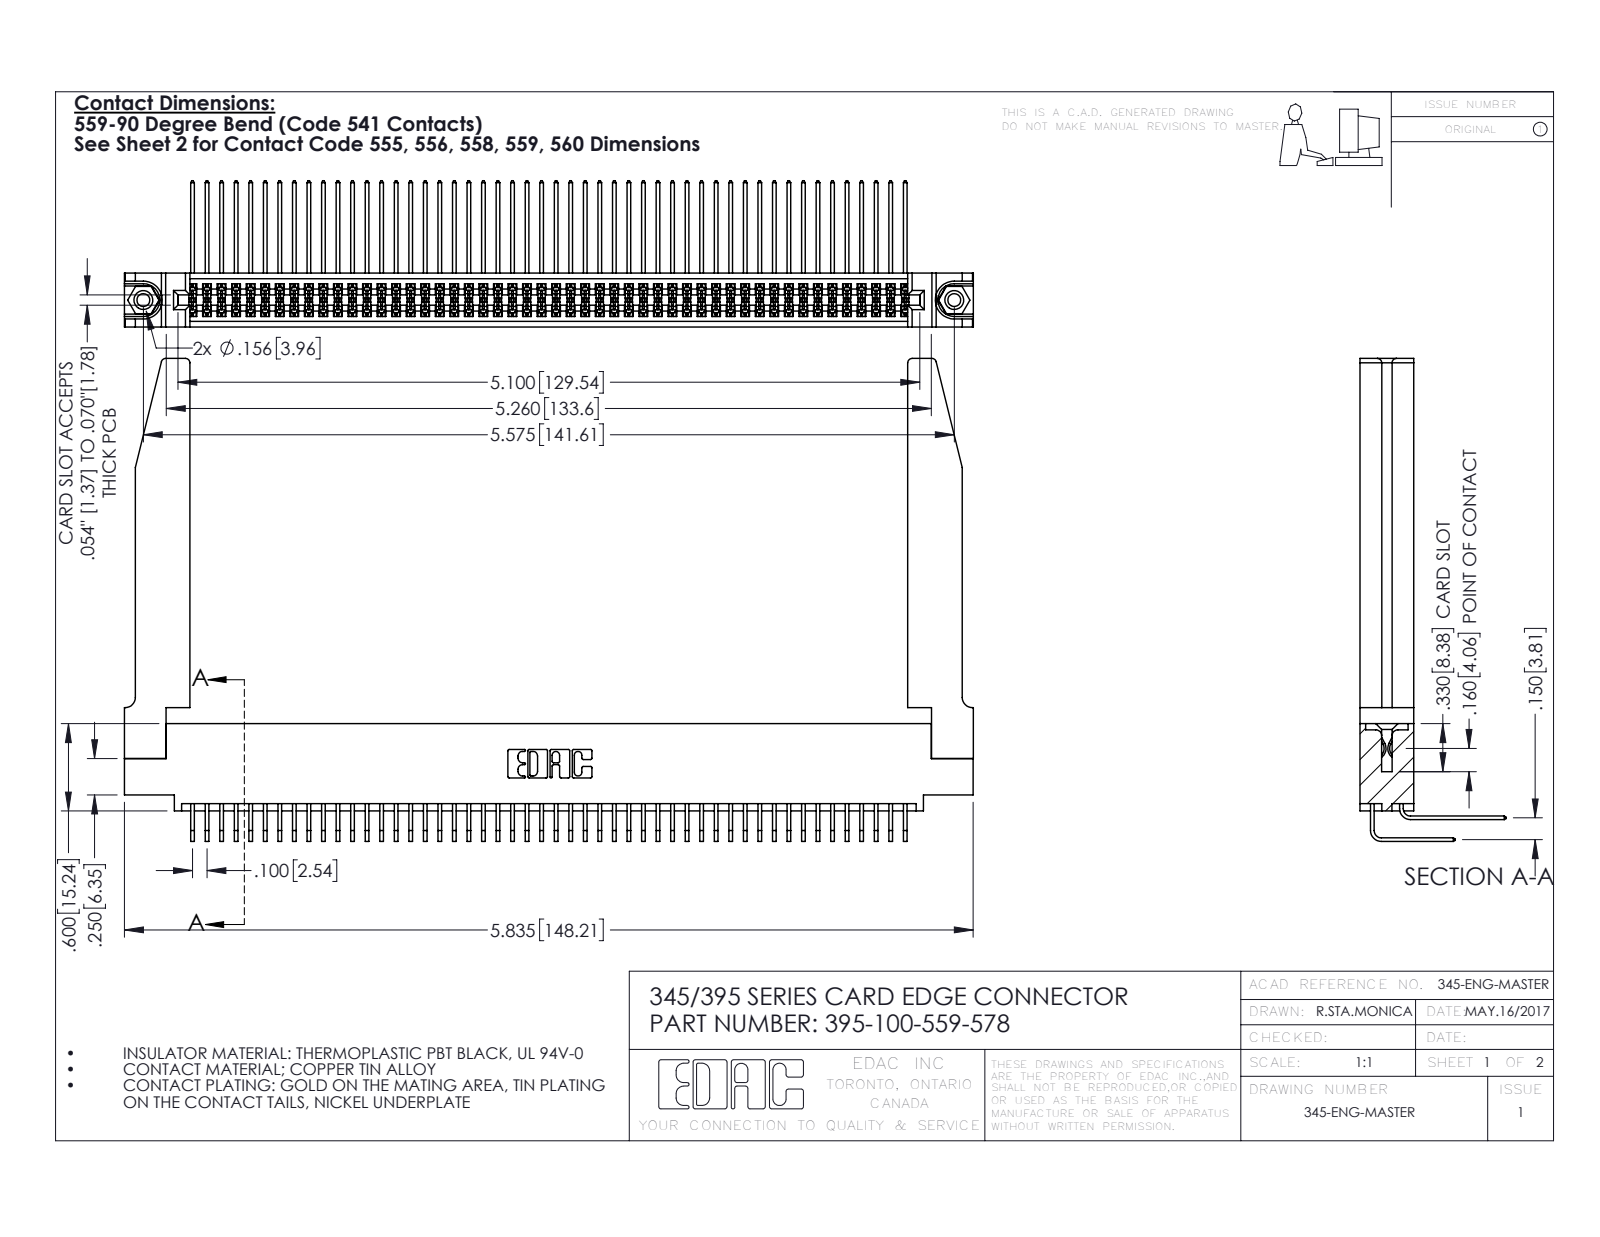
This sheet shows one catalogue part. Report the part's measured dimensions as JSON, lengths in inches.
{"part_name": "345-250-001_345-250-001-102; 345-292-001_559 Tail - 2; 395-100-559-578; 345 Part_0.110 Offset - 0.156 Dia-TH (+2 more)", "step_written_by": "SolidWorks 2016 (CONFIG_CONTROL_DESIGN)", "units": "inches", "bodies": {"solids": 105, "faces": 5564, "planar": 3726, "cylindrical": 1786, "other": 52}, "overall_size": [5.836, 3.319, 1.005], "volume_in3": 1.388, "surface_area_in2": 49.5, "round_holes": [[0.089, 2], [0.125, 2], [0.156, 2], [0.064, 1]], "round_bosses_or_shafts": [[0.155, 2]], "partial_cylinders_radius": [[0.006, 151], [0.01, 22], [0.03, 8], [0.007, 6], [0.031, 6], [0.026, 3], [0.014, 2], [0.019, 2]], "face_to_face_distances": [0.072, 0.37, 0.298, 0.098, 0.272, 0.025, 0.2, 0.225, 0.175, 0.15], "hole_center_spacings": [0.27, 5.339, 5.575]}
